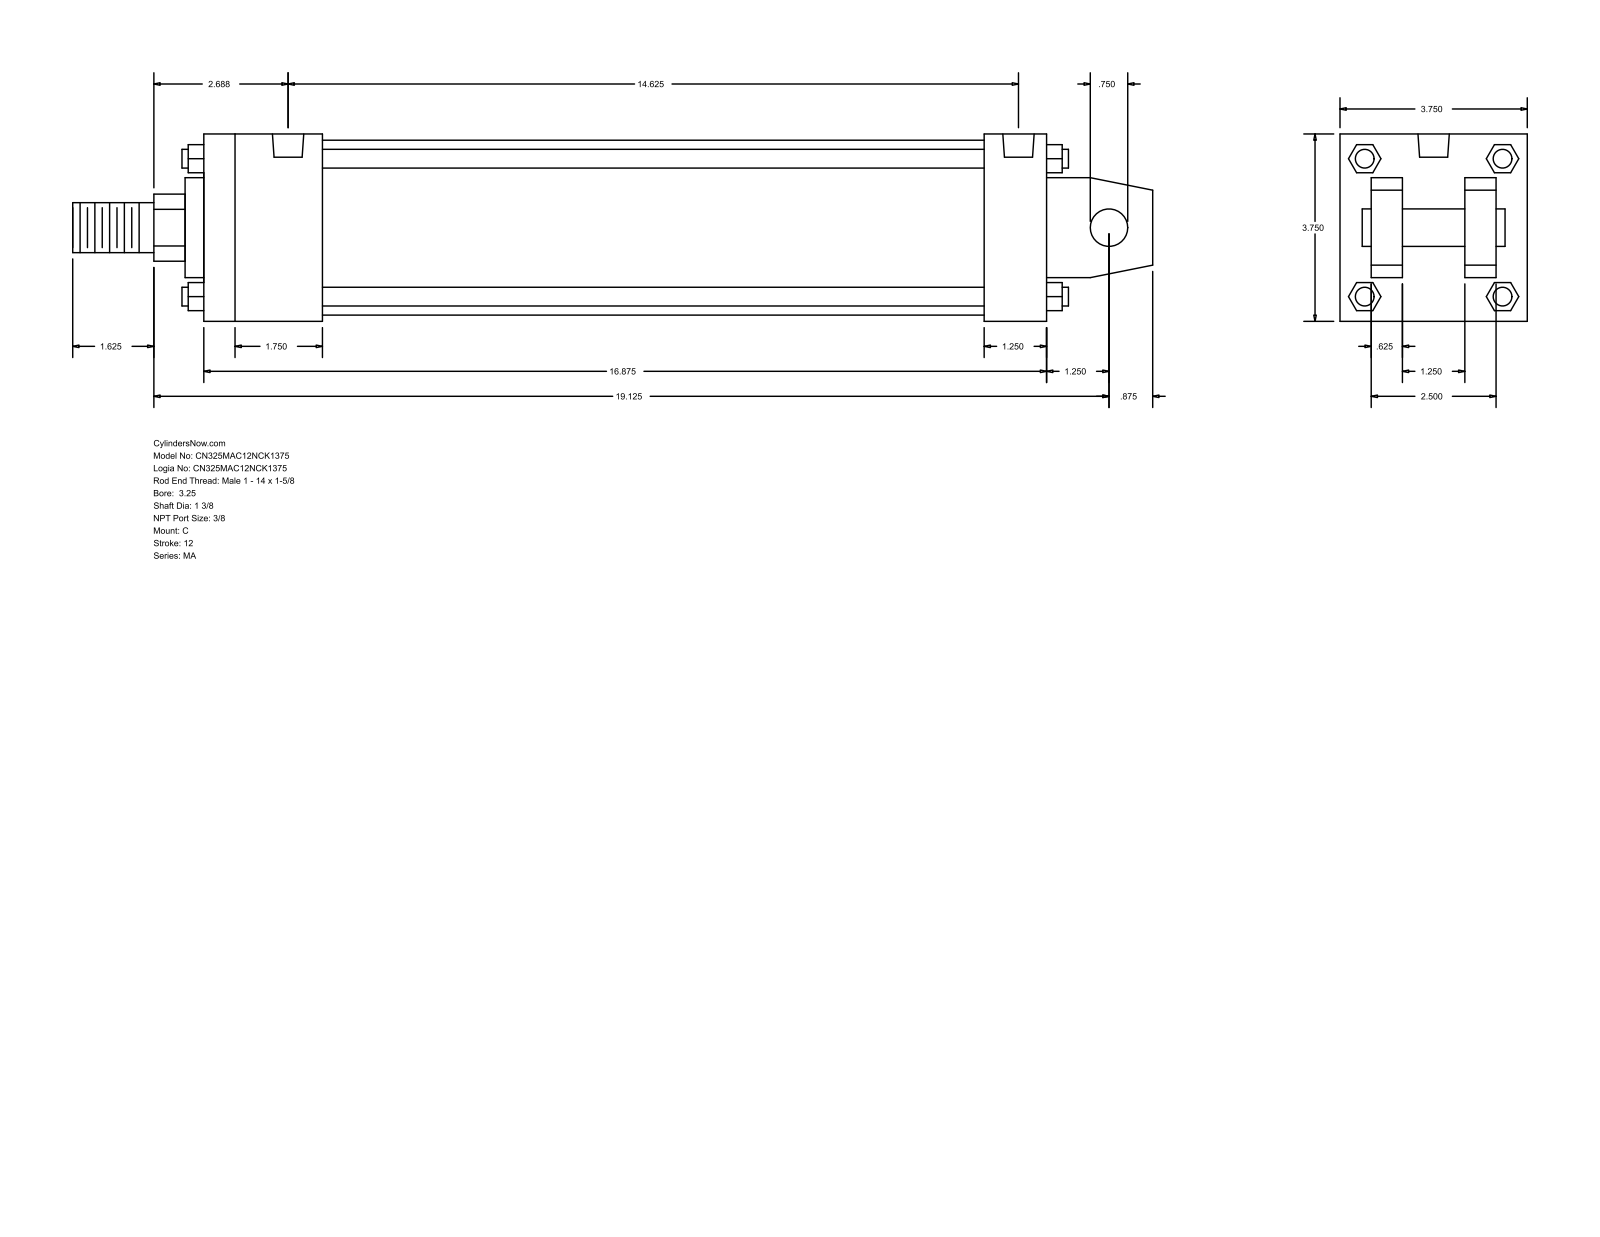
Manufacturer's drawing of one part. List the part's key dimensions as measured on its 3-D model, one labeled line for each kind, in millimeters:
Part name (STEP PRODUCT): MA_C__0325_1.375
STEP written by: GSSL Pune (CONFIG_CONTROL_DESIGN)
Units: millimetres
Bodies: 0 solids, 139 faces (108 planar, 31 cylindrical, 0 other)
Overall size (bounding box): 549.27 × 95.25 × 95.25
Round holes (diameter × count): ⌀11.11 ×4, ⌀15.93 ×2
Round bosses / shafts (diameter × count): ⌀9.53 ×4, ⌀88.9 ×1, ⌀50.8 ×1, ⌀34.92 ×1, ⌀25.4 ×1, ⌀19.05 ×1
Partial cylindrical surfaces — rounded edges, fillets, slot ends (radius × count): R17.06 ×1
Main face-to-face distances: 95.24, 15.87, 63.5, 428.62, 31.74, 79.37, 47.63, 396.87, 31.75, 60.32
Hole centre spacings: 361.95, 4.76, 4.77, 366.71, 366.72, 371.48
